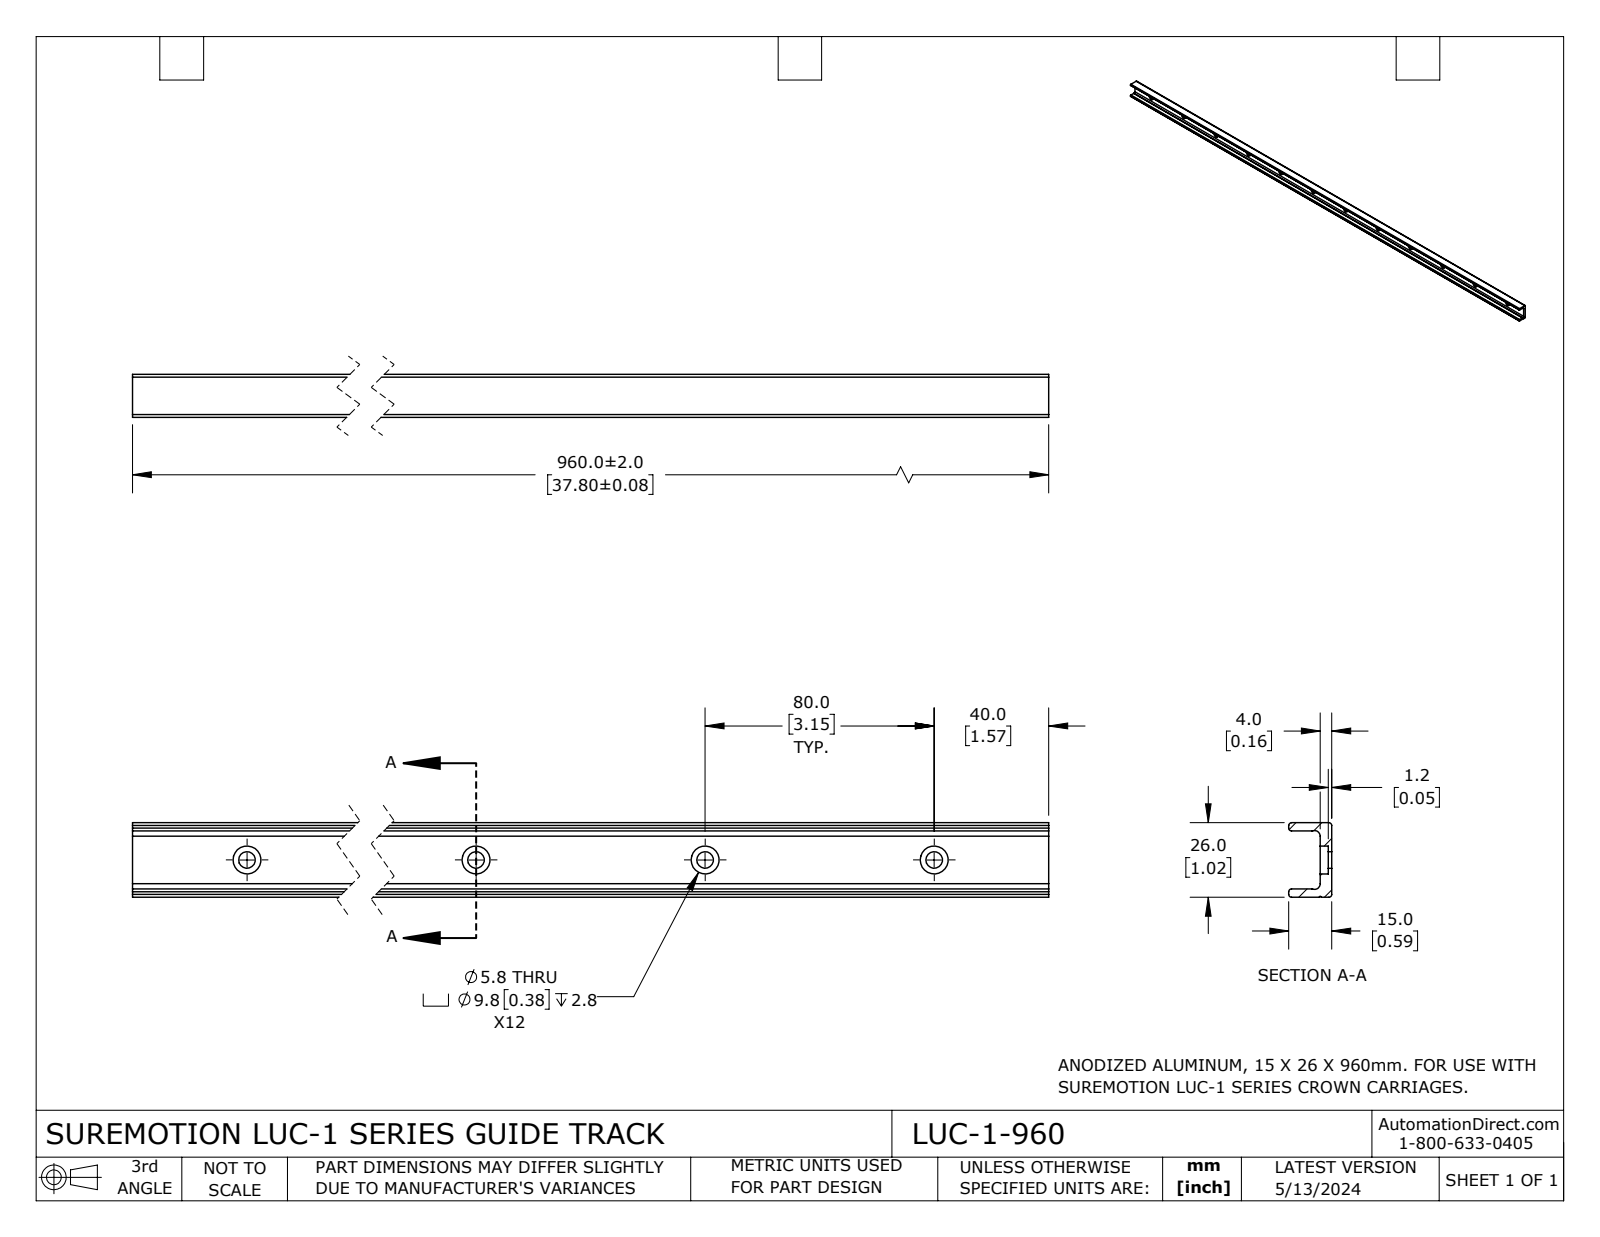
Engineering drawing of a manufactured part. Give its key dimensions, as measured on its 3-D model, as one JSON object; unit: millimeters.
{"part_name": "LUC-1-960", "step_written_by": "SolidWorks 2023 (CONFIG_CONTROL_DESIGN)", "units": "millimeters", "bodies": {"solids": 1, "faces": 82, "planar": 23, "cylindrical": 59, "other": 0}, "overall_size": [960, 26.01, 15.01], "volume_mm3": 157896, "surface_area_mm2": 97475, "round_holes": [[5.79, 12], [9.75, 12]], "partial_cylinders_radius": [[0.99, 8], [1.98, 2], [0.33, 1]], "face_to_face_distances": [4.01, 2.9, 23.12, 26.02, 20.22, 15.02, 11.01, 1.21, 2.8, 13.81], "hole_center_spacings": [80, 160, 240, 320, 400, 480, 560, 640]}
